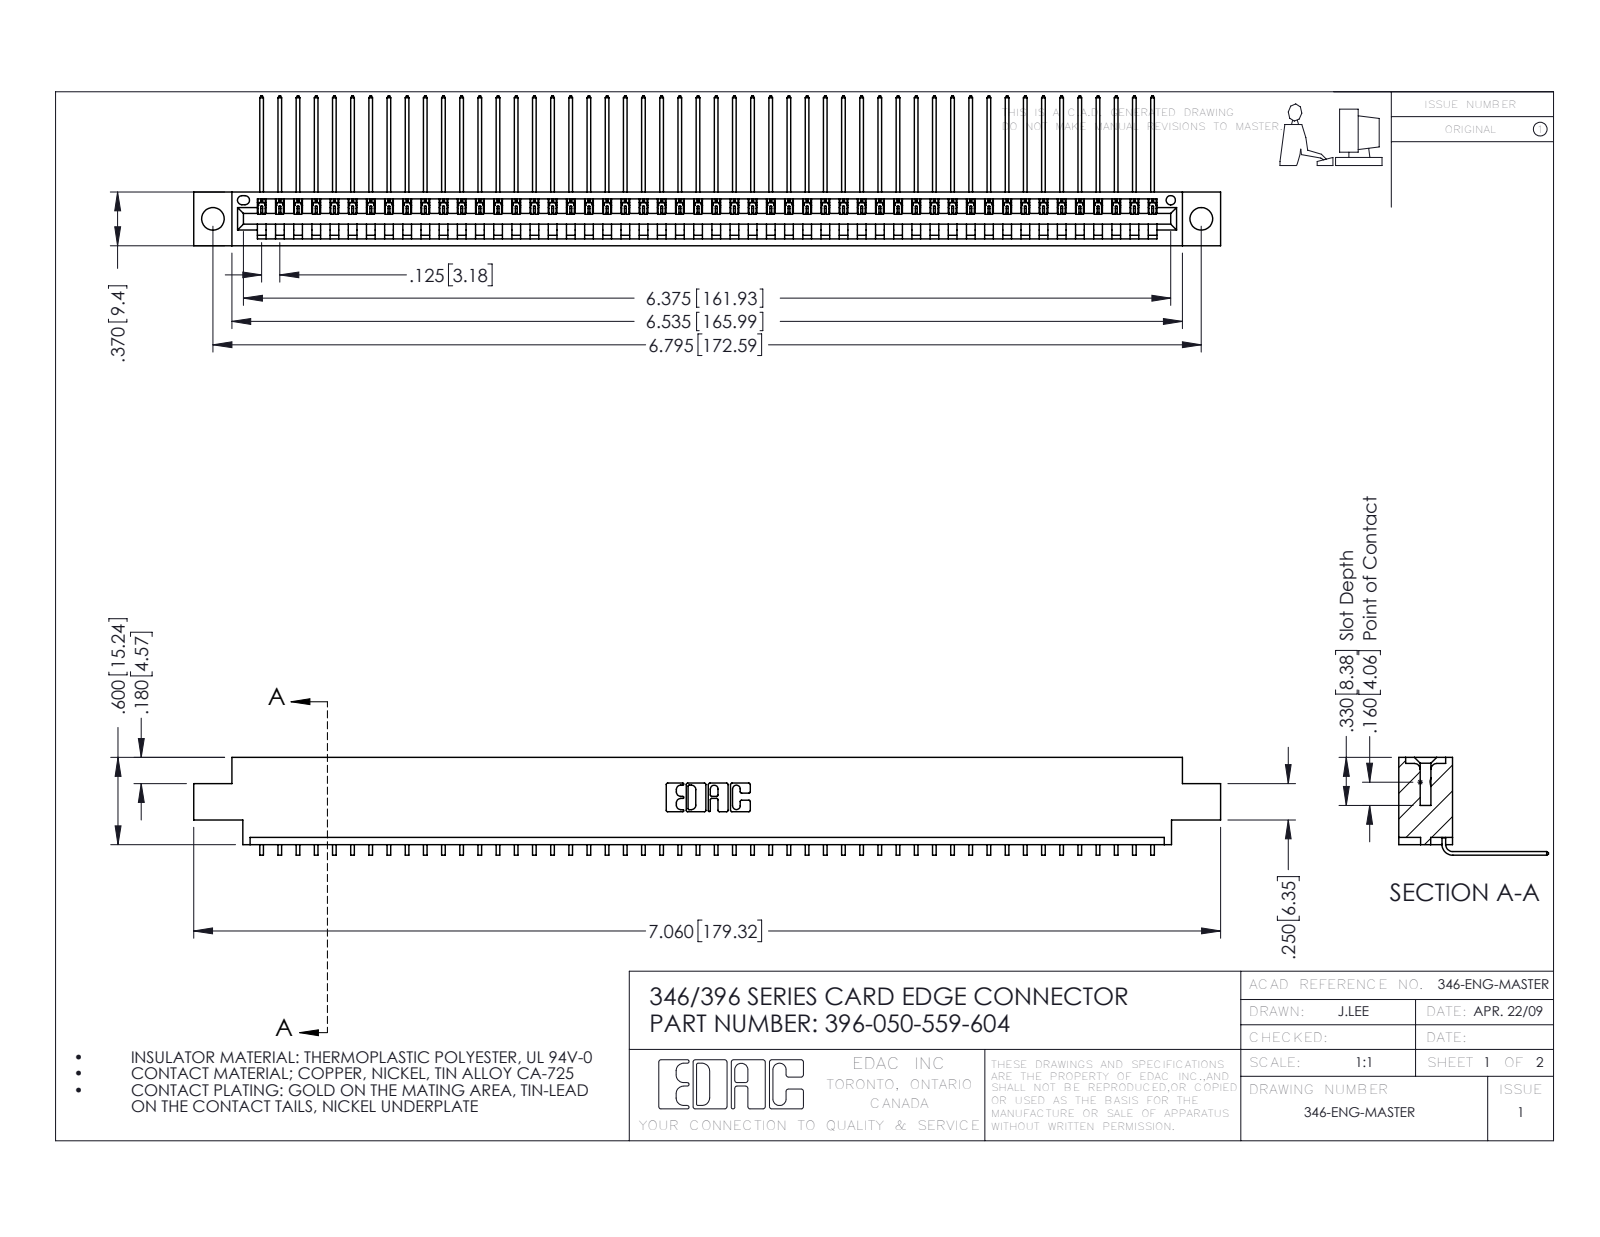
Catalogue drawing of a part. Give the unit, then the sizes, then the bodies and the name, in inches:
Units: inches
Overall size (bounding box): 7.06 × 1.03 × 0.673
Round holes (diameter × count): ⌀0.156 ×2, ⌀0.064 ×1
Partial cylindrical surfaces — rounded edges, fillets, slot ends (radius × count): R0.006 ×100, R0.01 ×22, R0.007 ×6, R0.031 ×6, R0.026 ×3, R0.031 ×2, R0.04 ×2, R0.014 ×1
Main face-to-face distances: 0.048, 0.322, 0.37, 0.025, 0.25, 0.072, 0.298, 0.148, 0.222, 0.1
Hole centre spacings: 0.246, 6.586, 6.795
Volume: 1.046 in³ · Surface area: 34.83 in²
Bodies: 51 solids, 3126 faces (2180 planar, 946 cylindrical, 0 other)
Part name (STEP PRODUCT): 396-050-559-604; 345-292-001_558 559 Tail - 1; 346 Part_0.170 Offset - 0.156 Dia-TH
STEP written by: SolidWorks 2016 (CONFIG_CONTROL_DESIGN)
